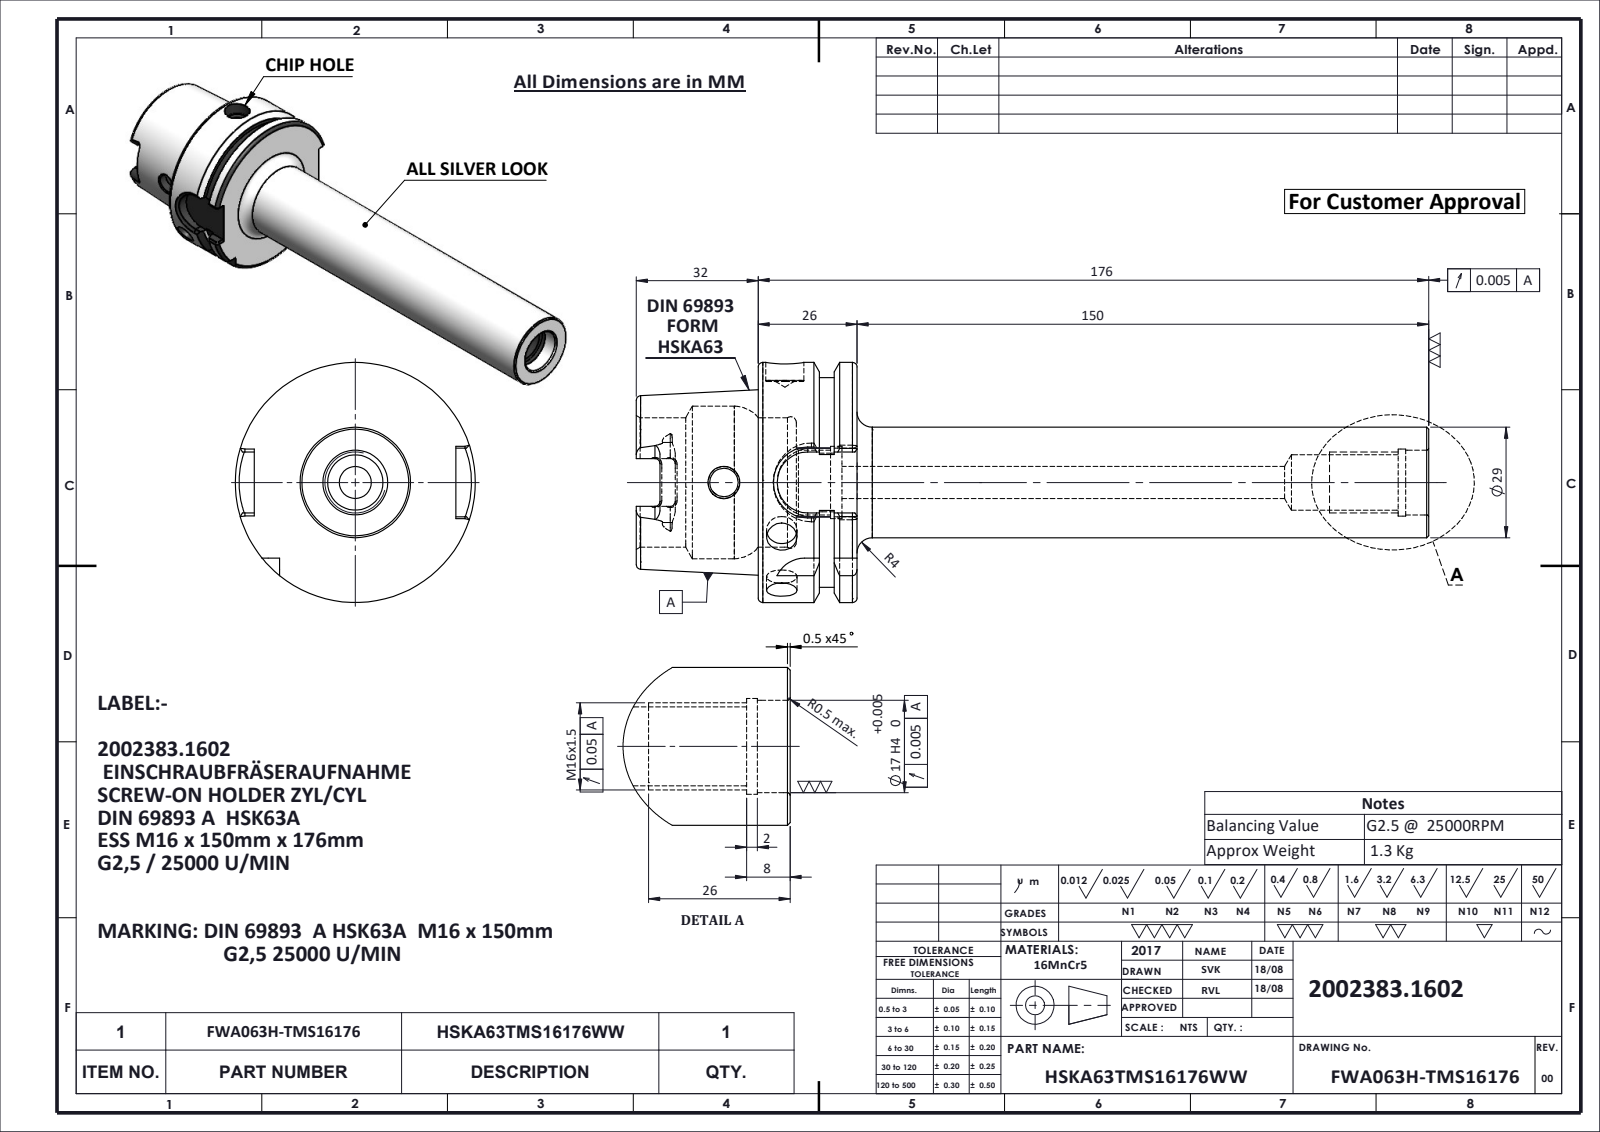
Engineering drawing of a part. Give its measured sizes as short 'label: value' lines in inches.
name: HSKA63TMS16176WW; FWA063H-TMS16176
written by: SolidWorks 2024 (CONFIG_CONTROL_DESIGN)
unit: in
bodies: 1 solid, 168 faces (51 planar, 53 cylindrical, 64 other)
size: 8.189 × 2.48 × 2.48
volume: 10.21 in³; area: 62.84 in²
holes: 2× ⌀0.315, 1× ⌀0.295, 1× ⌀0.331, 1× ⌀0.394, 1× ⌀0.571, 1× ⌀0.669, 1× ⌀0.693, 1× ⌀0.748, 1× ⌀1.339, 1× ⌀1.575
bosses: 1× ⌀2.48, 1× ⌀2.165, 1× ⌀1.142
rounds: 6× R0.051, 4× R0.113, 2× R0.315, 1× R0.354
face distances: 1.022, 0.394, 0.628, 1.26, 1.654, 2.281, 8.189, 6.929, 6.535, 5.907
